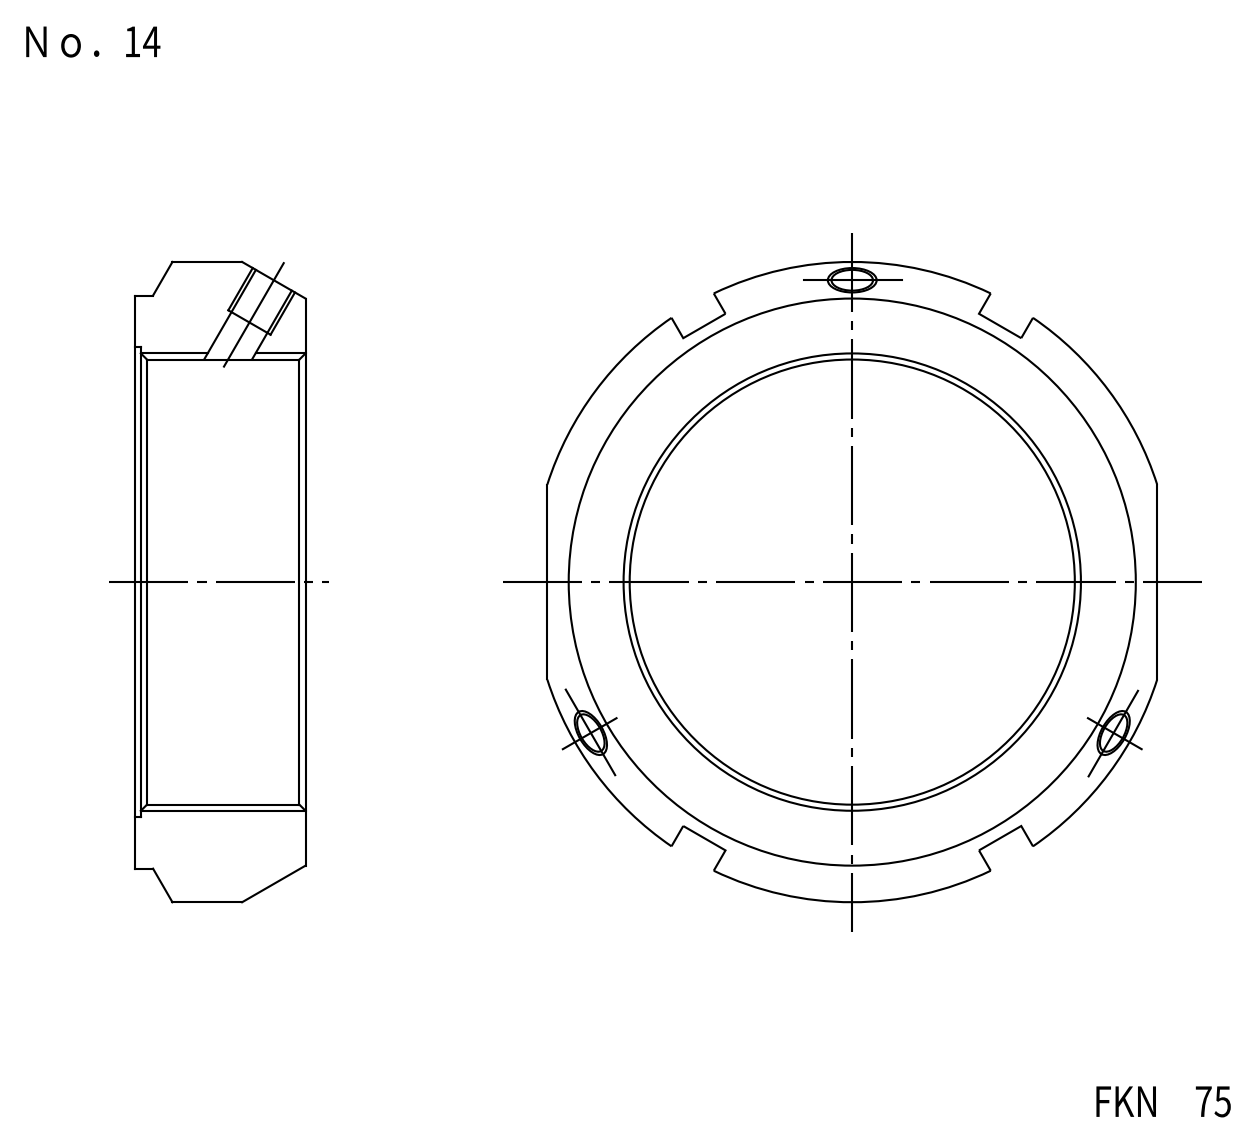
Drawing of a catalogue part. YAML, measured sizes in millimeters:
part_name: "FKD FKN75"
step_written_by: "Autodesk Inventor LT (CONFIG_CONTROL_DESIGN)"
units: millimeters
bodies: {solids: 1, faces: 37, planar: 20, cylindrical: 15, other: 2}
overall_size: [105, 100, 28]
volume: 95687
surface_area: 22761
round_holes:
  - {diameter: 6.65, count: 3}
  - {diameter: 8.1, count: 3}
  - {diameter: 75, count: 1}
  - {diameter: 77, count: 1}
round_bosses_or_shafts:
  - {diameter: 94, count: 1}
partial_cylinders:
  - {radius: 52.5, count: 1}
face_to_face_distances: [28, 100, 97, 8, 1.5, 26.5]
